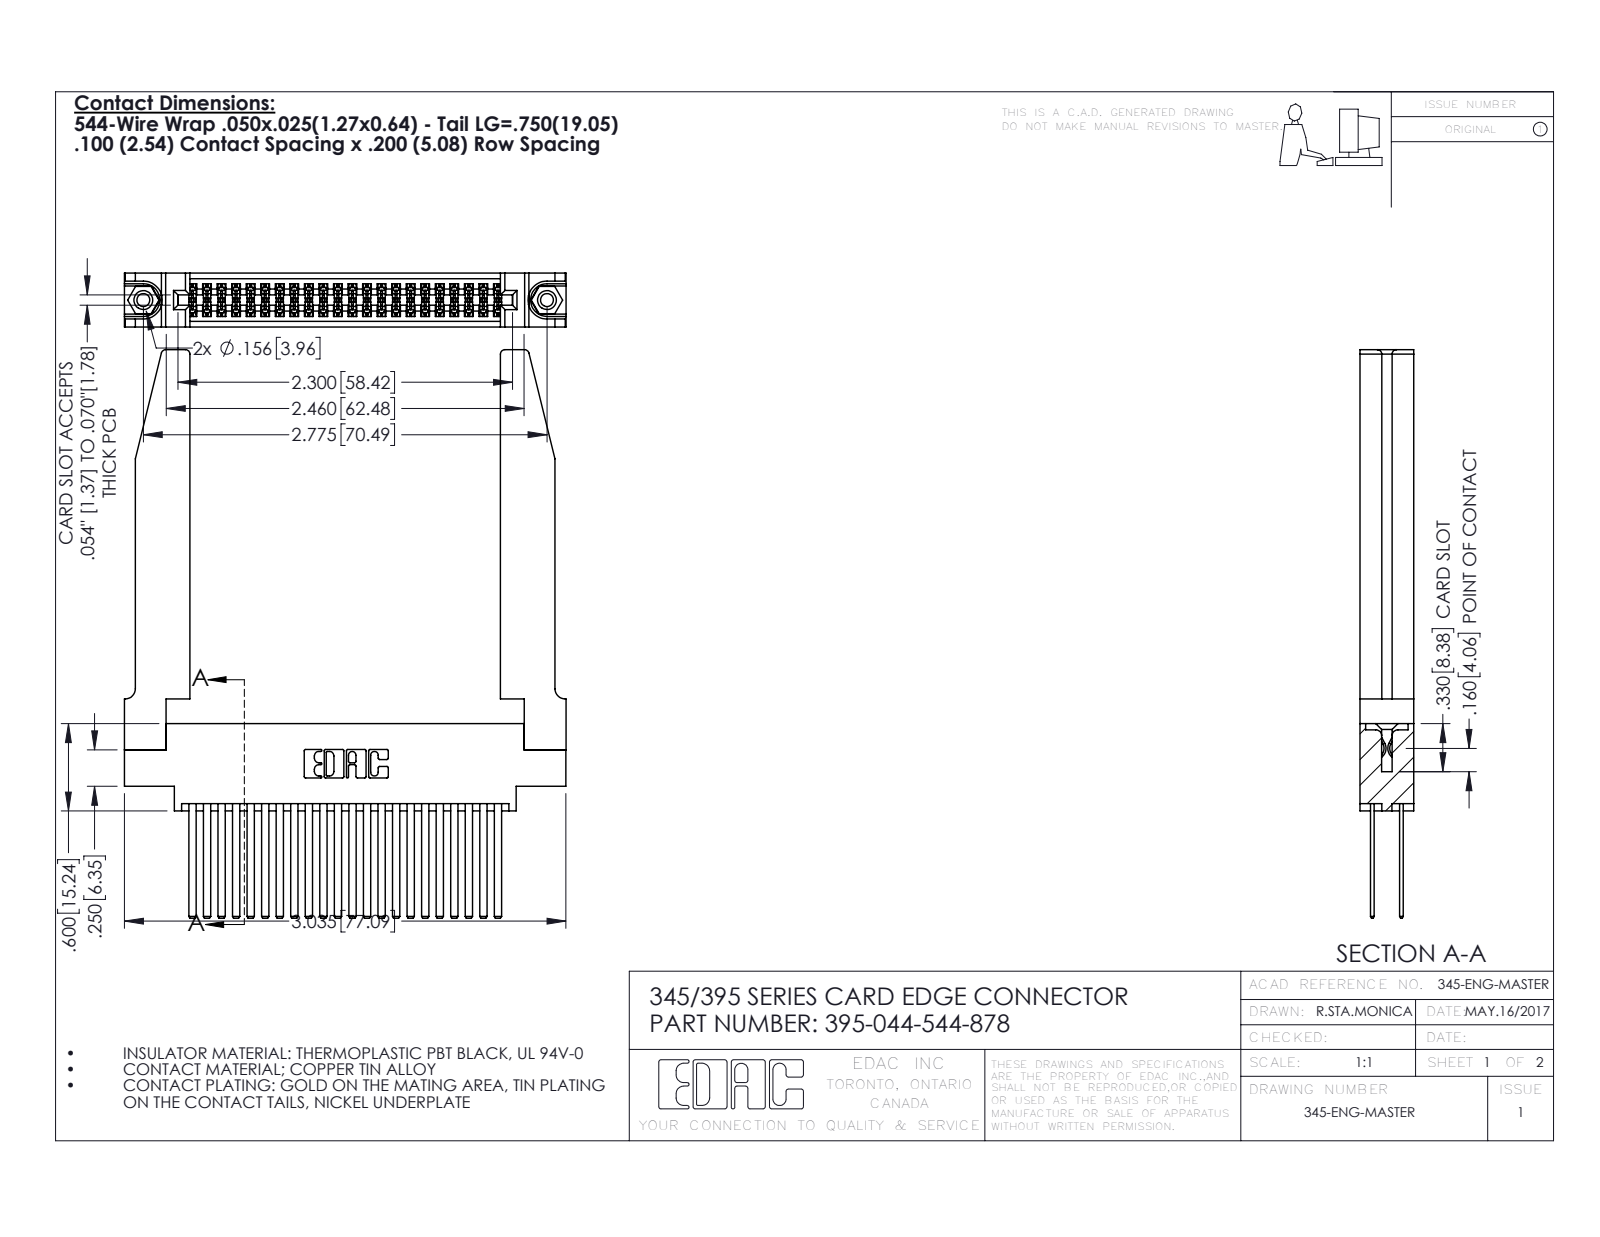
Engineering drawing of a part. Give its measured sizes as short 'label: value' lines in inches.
name: 345-220-078_345-220-078; 345 Part_0.170 Offset - 0.156 Dia-TH; 395-044-544-878; 345-292-001_345-293-144 (+1 more)
written by: SolidWorks 2016 (CONFIG_CONTROL_DESIGN)
unit: in
bodies: 49 solids, 2300 faces (1502 planar, 746 cylindrical, 52 other)
size: 3.907 × 3.036 × 0.37
volume: 0.951 in³; area: 30.91 in²
holes: 2× ⌀0.089, 2× ⌀0.125, 2× ⌀0.156, 1× ⌀0.064
bosses: 2× ⌀0.155
rounds: 66× R0.006, 22× R0.01, 8× R0.03, 6× R0.007, 6× R0.031, 3× R0.026, 2× R0.014, 2× R0.019
face distances: 0.072, 0.298, 0.37, 0.098, 0.272, 0.025, 0.2, 0.225, 0.175, 0.148
hole spacings: 0.27, 2.541, 2.775
